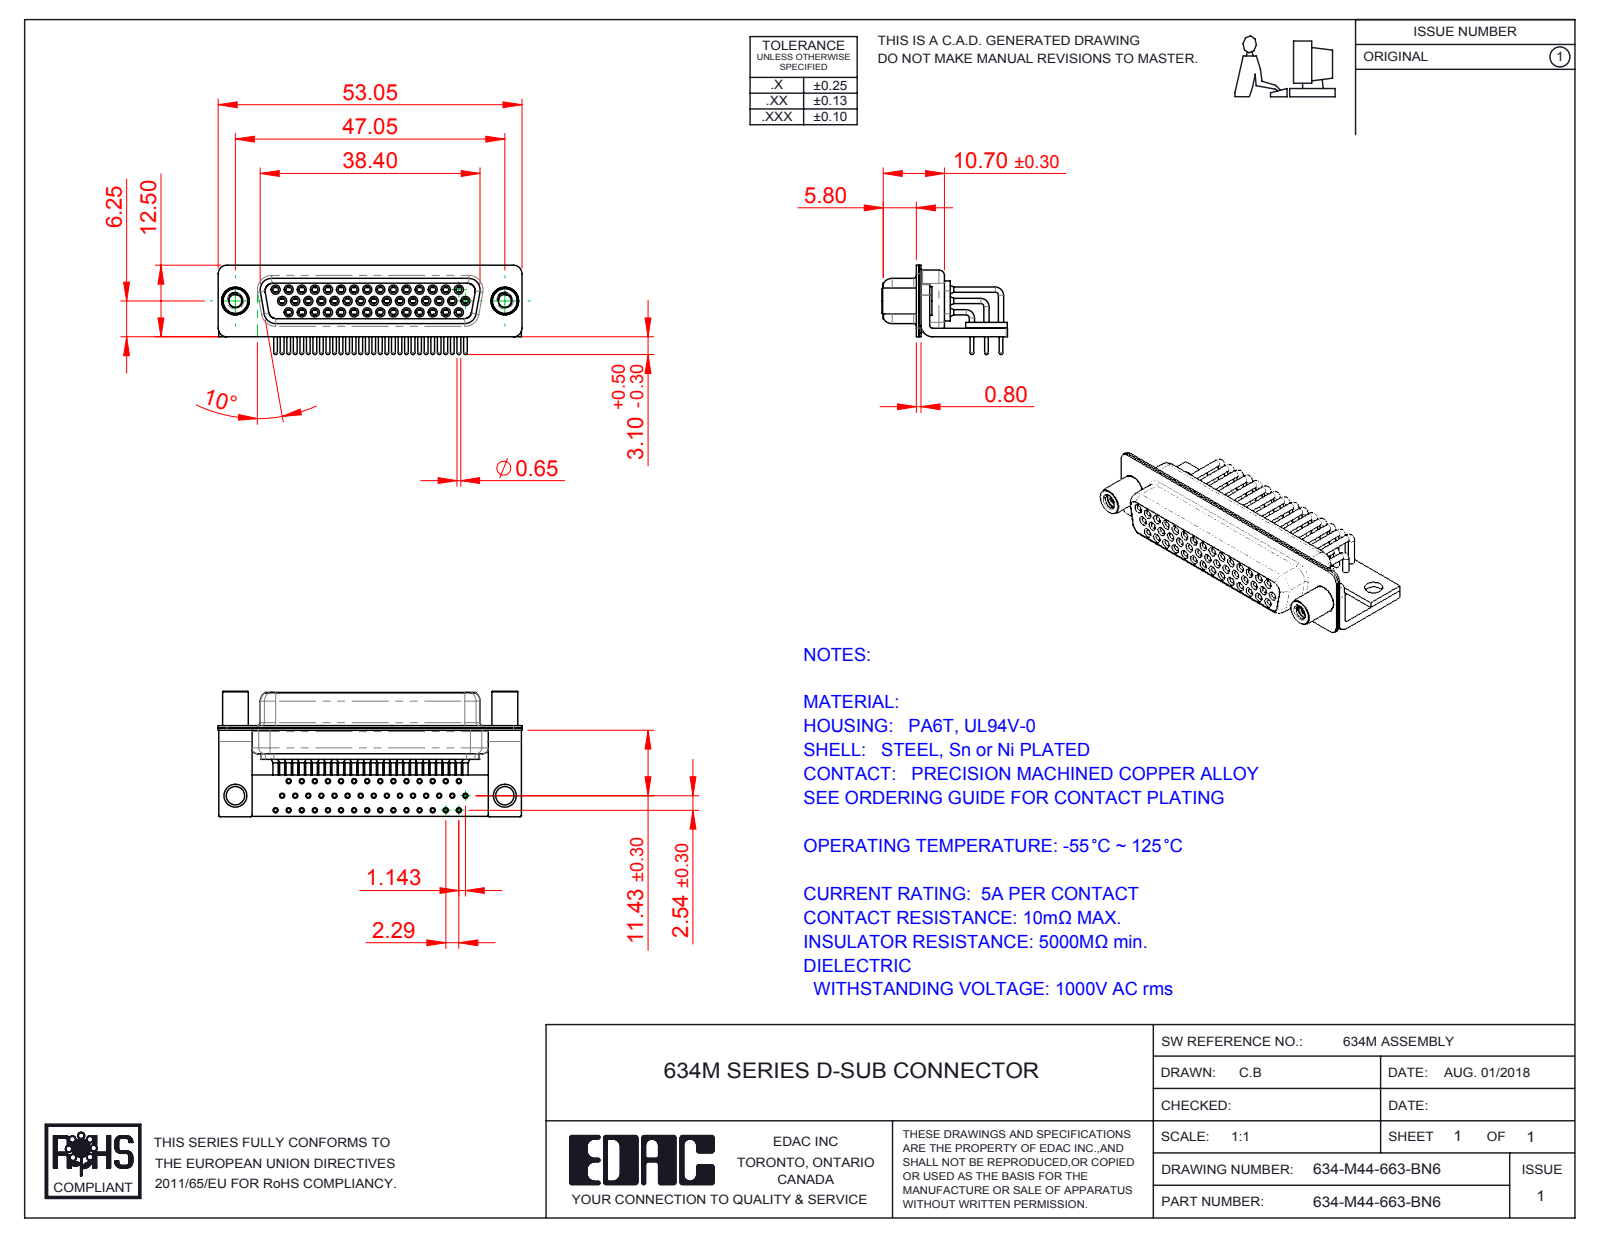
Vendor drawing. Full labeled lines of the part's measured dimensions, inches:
Part name (STEP PRODUCT): 634M Contact Row 3; 634M Contact Row 1; 634M Housing_44 Contacts; 634-M44-663-BN6 (+6 more)
STEP written by: SolidWorks 2016 (CONFIG_CONTROL_DESIGN)
Units: inches
Bodies: 52 solids, 2799 faces (755 planar, 1301 cylindrical, 743 other)
Overall size (bounding box): 2.089 × 0.862 × 0.614
Volume: 0.28 in³ · Surface area: 23.12 in²
Round holes (diameter × count): ⌀0.035 ×44, ⌀0.039 ×44, ⌀0.043 ×44, ⌀0.067 ×44, ⌀0.071 ×44, ⌀0.079 ×44, ⌀0.089 ×2, ⌀0.126 ×2, ⌀0.157 ×2, ⌀0.189 ×2
Round bosses / shafts (diameter × count): ⌀0.063 ×44, ⌀0.059 ×44, ⌀0.035 ×44, ⌀0.026 ×44, ⌀0.197 ×2, ⌀0.193 ×2, ⌀0.177 ×2
Partial cylindrical surfaces — rounded edges, fillets, slot ends (radius × count): R0.01 ×16, R0.059 ×16, R0.079 ×13, R0.053 ×8, R0.063 ×8, R0.02 ×5, R0.024 ×4, R0.026 ×4
Main face-to-face distances: 0.016, 0.091, 0.075, 0.039, 0.031, 0.335, 0.368, 0.057, 0.352, 0.059
Hole centre spacings: 0.09, 0.09, 0.18, 0.27, 0.45, 0.156, 0.324, 0.36
